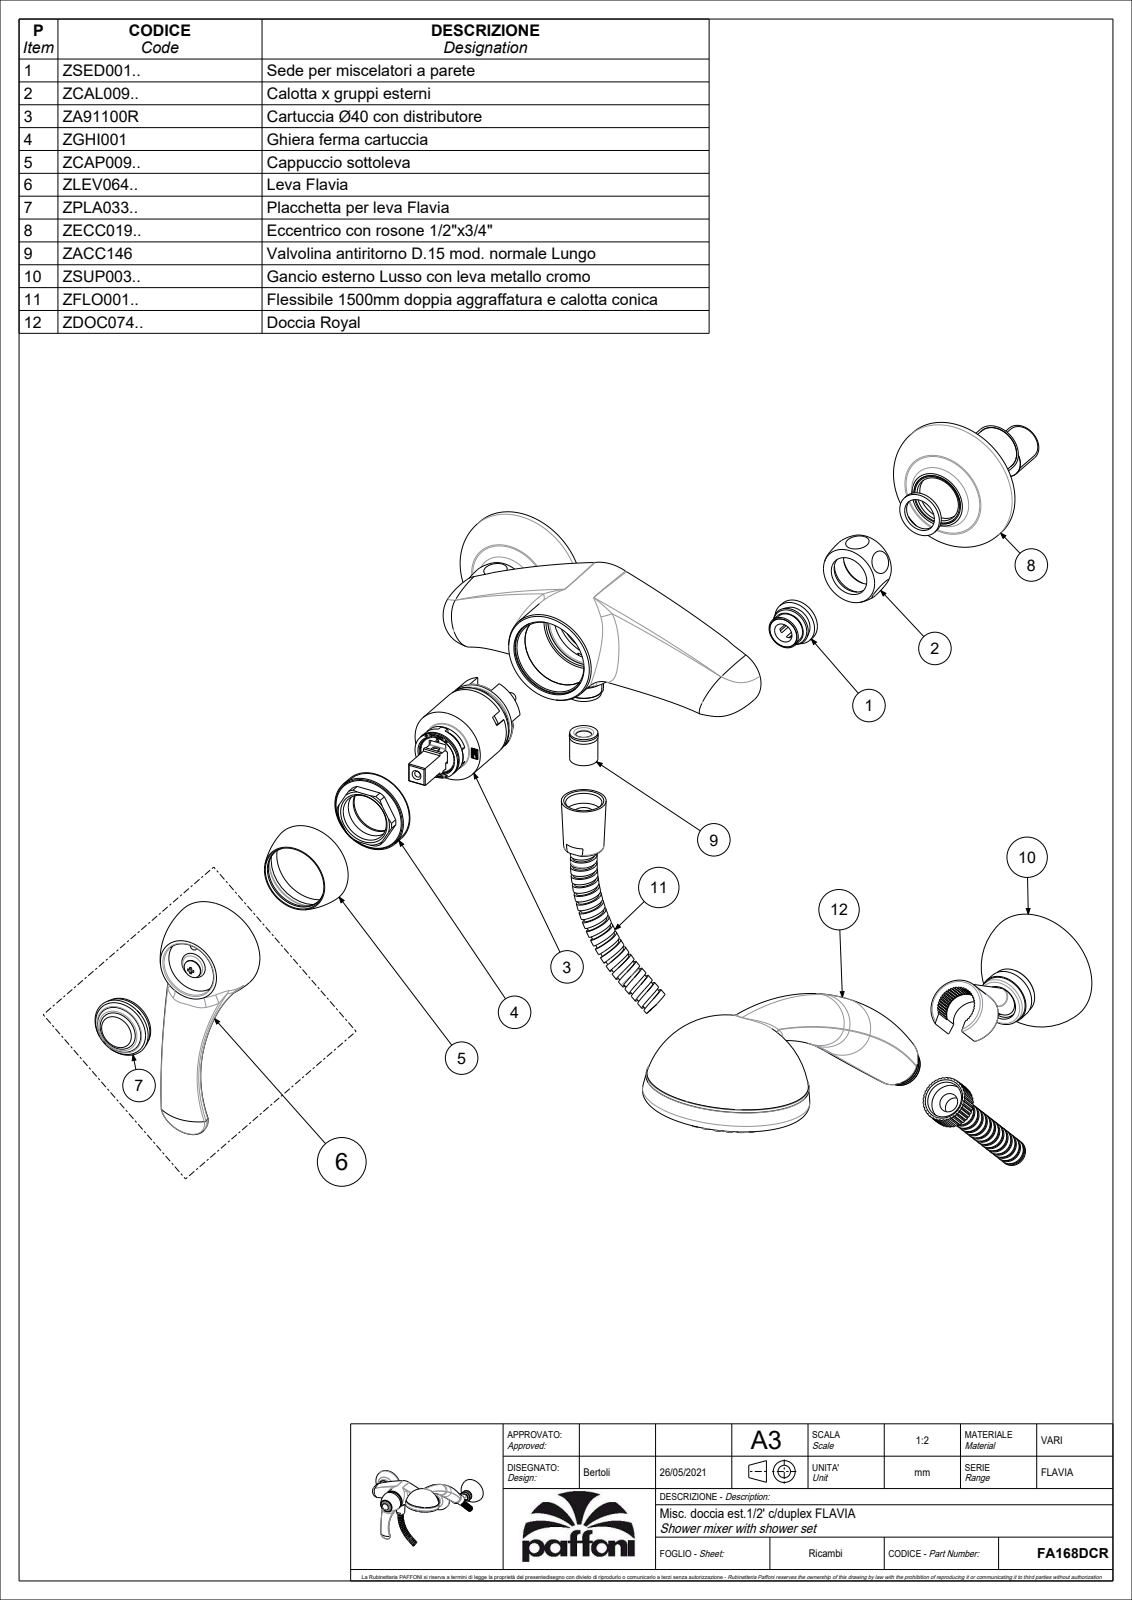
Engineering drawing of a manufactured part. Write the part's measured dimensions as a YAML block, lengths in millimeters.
part_name: "FA168DCR"
step_written_by: "CREO PARAMETRIC BY PTC INC, 2020044 (CONFIG_CONTROL_DESIGN)"
units: millimeters
bodies: {solids: 4, faces: 4659, planar: 1878, cylindrical: 1286, other: 1495}
overall_size: [334.06, 309.06, 258.38]
volume: 456141
surface_area: 297751
round_holes:
  - {diameter: 1.5, count: 40}
  - {diameter: 2.5, count: 16}
  - {diameter: 1.2, count: 12}
  - {diameter: 3.9, count: 12}
  - {diameter: 7.4, count: 12}
  - {diameter: 4.4, count: 4}
  - {diameter: 8, count: 4}
  - {diameter: 7, count: 3}
  - {diameter: 7.2, count: 3}
  - {diameter: 14, count: 3}
  - {diameter: 18, count: 3}
  - {diameter: 4, count: 2}
round_bosses_or_shafts:
  - {diameter: 4.4, count: 12}
  - {diameter: 2, count: 12}
  - {diameter: 13, count: 8}
  - {diameter: 6.2, count: 3}
  - {diameter: 70, count: 2}
  - {diameter: 28.14, count: 2}
  - {diameter: 27, count: 2}
  - {diameter: 24, count: 2}
partial_cylinders:
  - {radius: 0.5, count: 93}
  - {radius: 0.3, count: 37}
  - {radius: 0.2, count: 24}
  - {radius: 1.5, count: 24}
  - {radius: 1, count: 12}
  - {radius: 3.5, count: 12}
  - {radius: 1.6, count: 8}
  - {radius: 2.2, count: 8}
face_to_face_distances: [3.5, 3, 11.5, 0.5, 2, 13.4, 6.5, 2.5, 1, 13.5]
hole_center_spacings: [10.7, 15, 23.8, 10.61, 18.43, 16, 37.25, 8.19]
